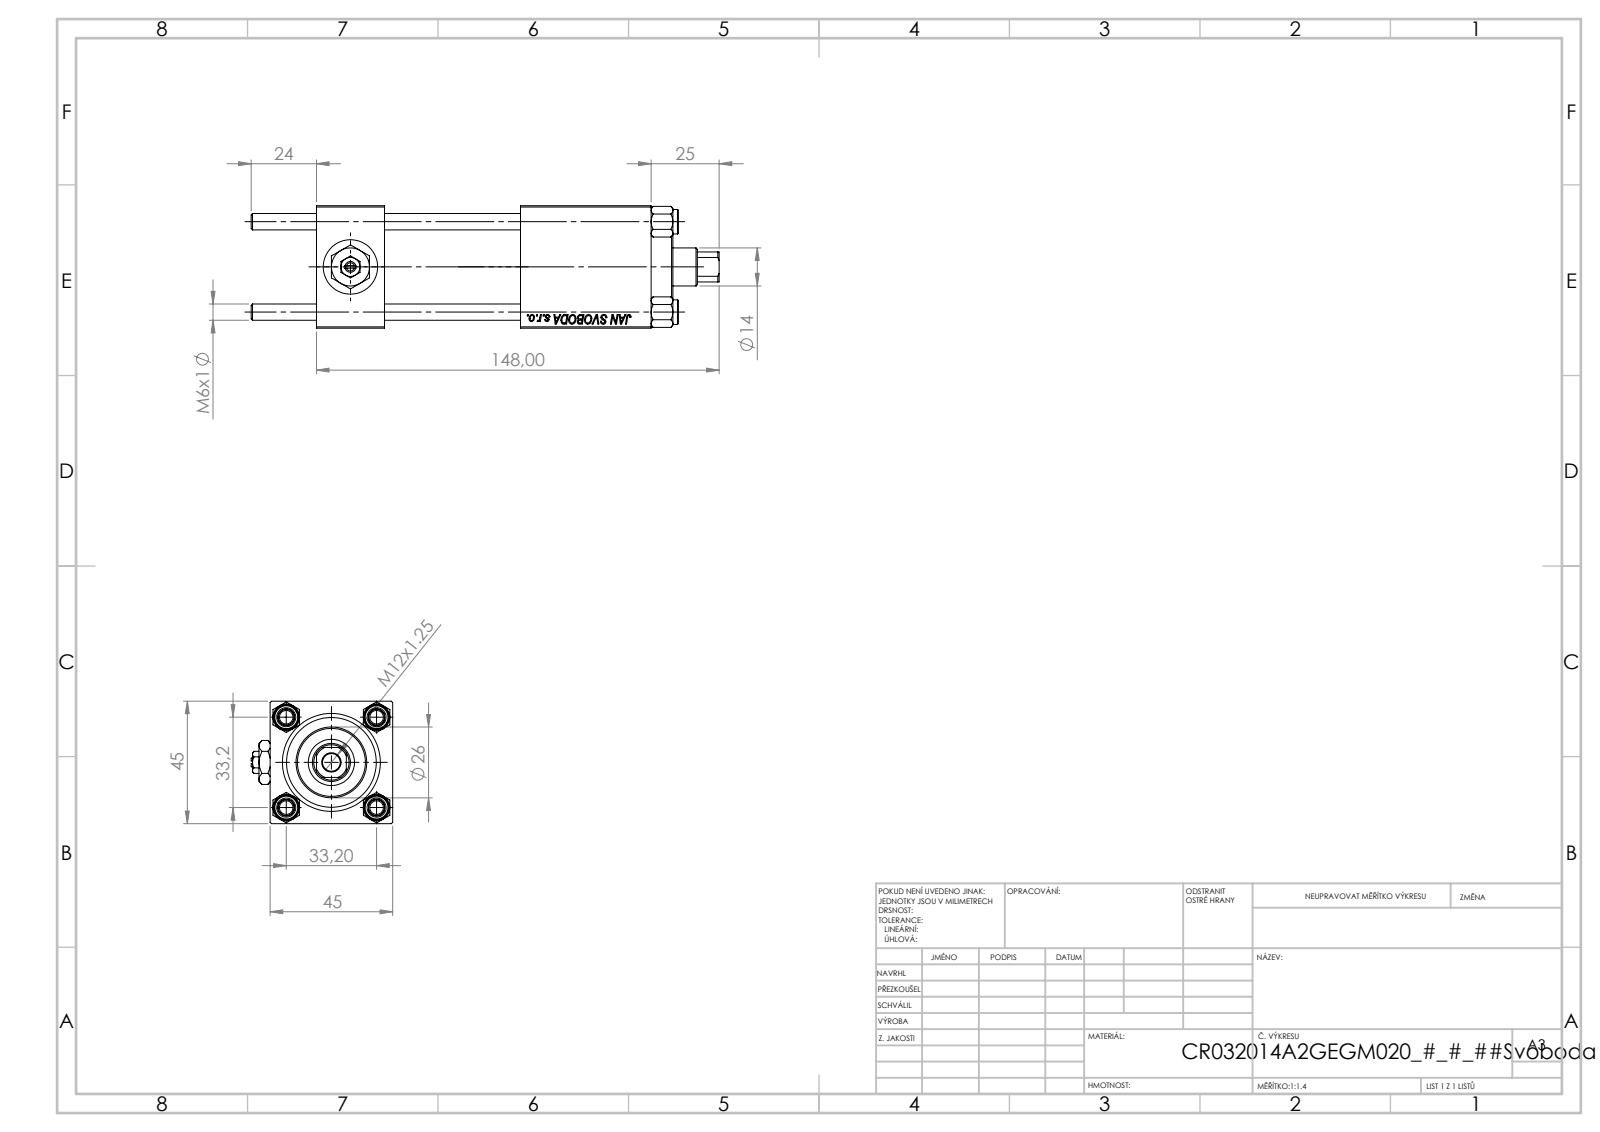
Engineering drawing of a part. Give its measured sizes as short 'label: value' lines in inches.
name: V215CR_VCP; Zatka_pro_OIL_PORT; NUT_M5; V215CR_BODY_A (+2 more)
written by: SolidWorks 2019 (CONFIG_CONTROL_DESIGN)
unit: in
bodies: 12 solids, 1184 faces (540 planar, 86 cylindrical, 558 other)
size: 6.772 × 2.047 × 1.772
volume: 12.03 in³; area: 114.6 in²
holes: 4× ⌀0.236, 2× ⌀0.276, 2× ⌀0.518, 2× ⌀0.787, 1× ⌀0.256, 1× ⌀0.512, 1× ⌀0.551, 1× ⌀0.669, 1× ⌀0.945, 1× ⌀1.26, 1× ⌀1.299
bosses: 4× ⌀0.354, 1× ⌀1.496, 1× ⌀1.024
rounds: 1× R0.256
face distances: 1.772, 0.984, 4.843, 3.858, 1.969, 2.953, 1.89, 3.713, 2.728, 0.76
hole spacings: 0.924, 1.307, 1.848, 2.972
